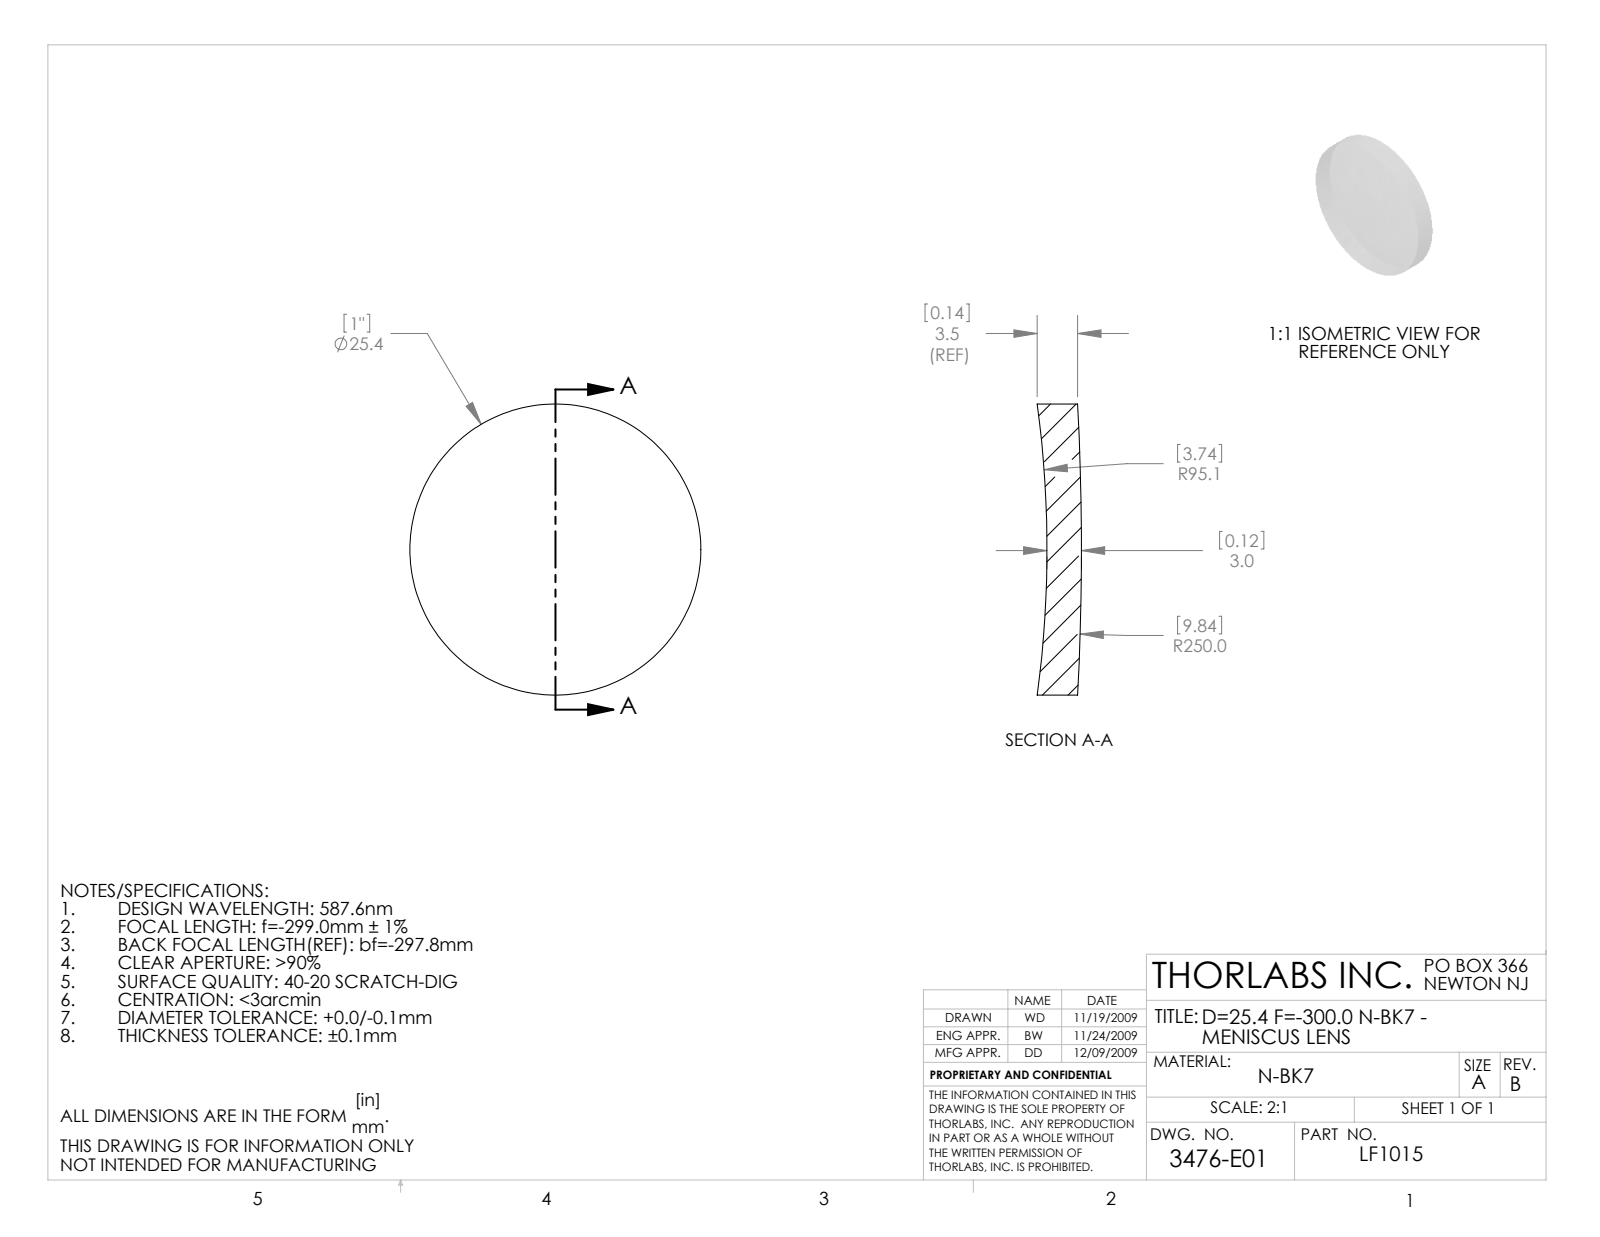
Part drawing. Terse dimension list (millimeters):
name: 3476-E0W
written by: SolidWorks 2009 (AUTOMOTIVE_DESIGN)
unit: mm
bodies: 1 solid, 6 faces (0 planar, 2 cylindrical, 4 other)
size: 25.4 × 25.4 × 3.85
volume: 1 654 mm³; area: 1 298 mm²
bosses: 1× ⌀25.4
